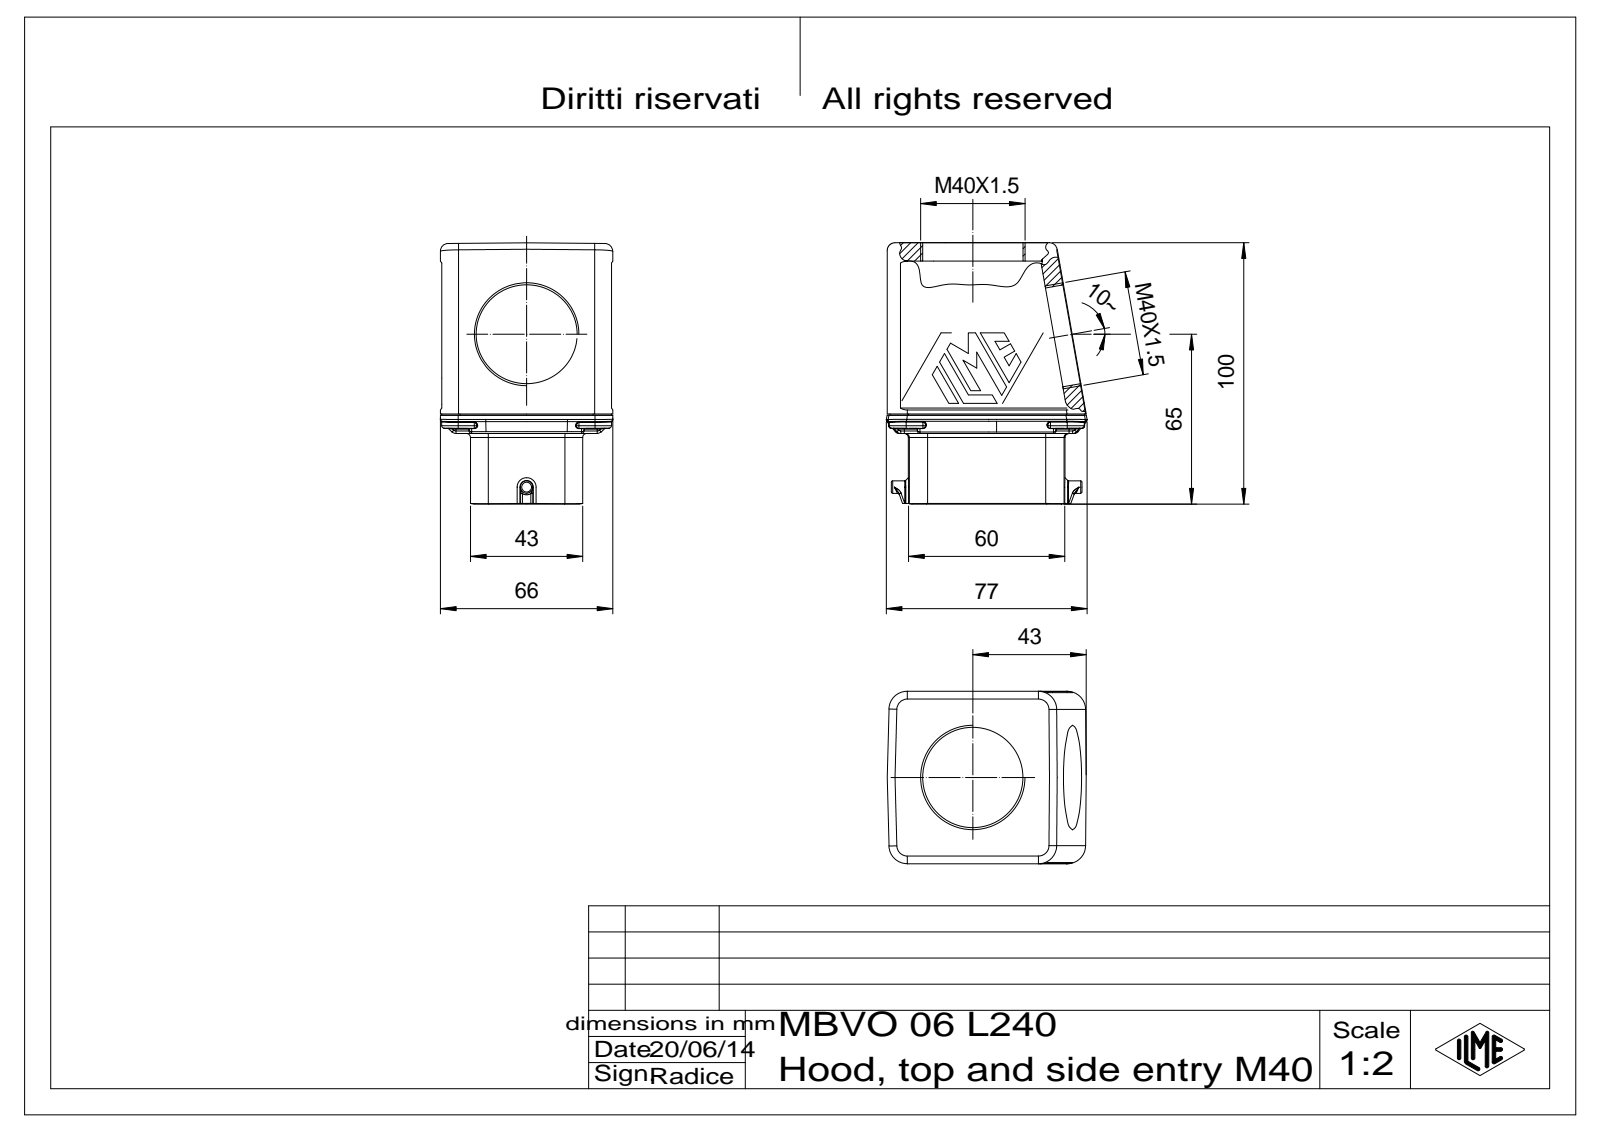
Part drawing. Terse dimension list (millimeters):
name: 53848_Body_1_Body_1.1
written by: CoCreate Modeling 16.00A 16-Aug-2008 (C) Parametric Technology GmbH (AUTOMOTIVE_DESIGN)
unit: mm
bodies: 1 solid, 564 faces (266 planar, 142 cylindrical, 156 other)
size: 99.49 × 75.76 × 66.01
volume: 300 284 mm³; area: 43 116 mm²
holes: 2× ⌀40
bosses: 1× ⌀4.8
rounds: 46× R1, 18× R0.3, 14× R7, 10× R3, 6× R1.5, 4× R0.5, 4× R4.2, 4× R5
face distances: 72.73, 65.01, 0.4, 65.41, 18, 54.73, 17.78, 11, 54.01, 54
